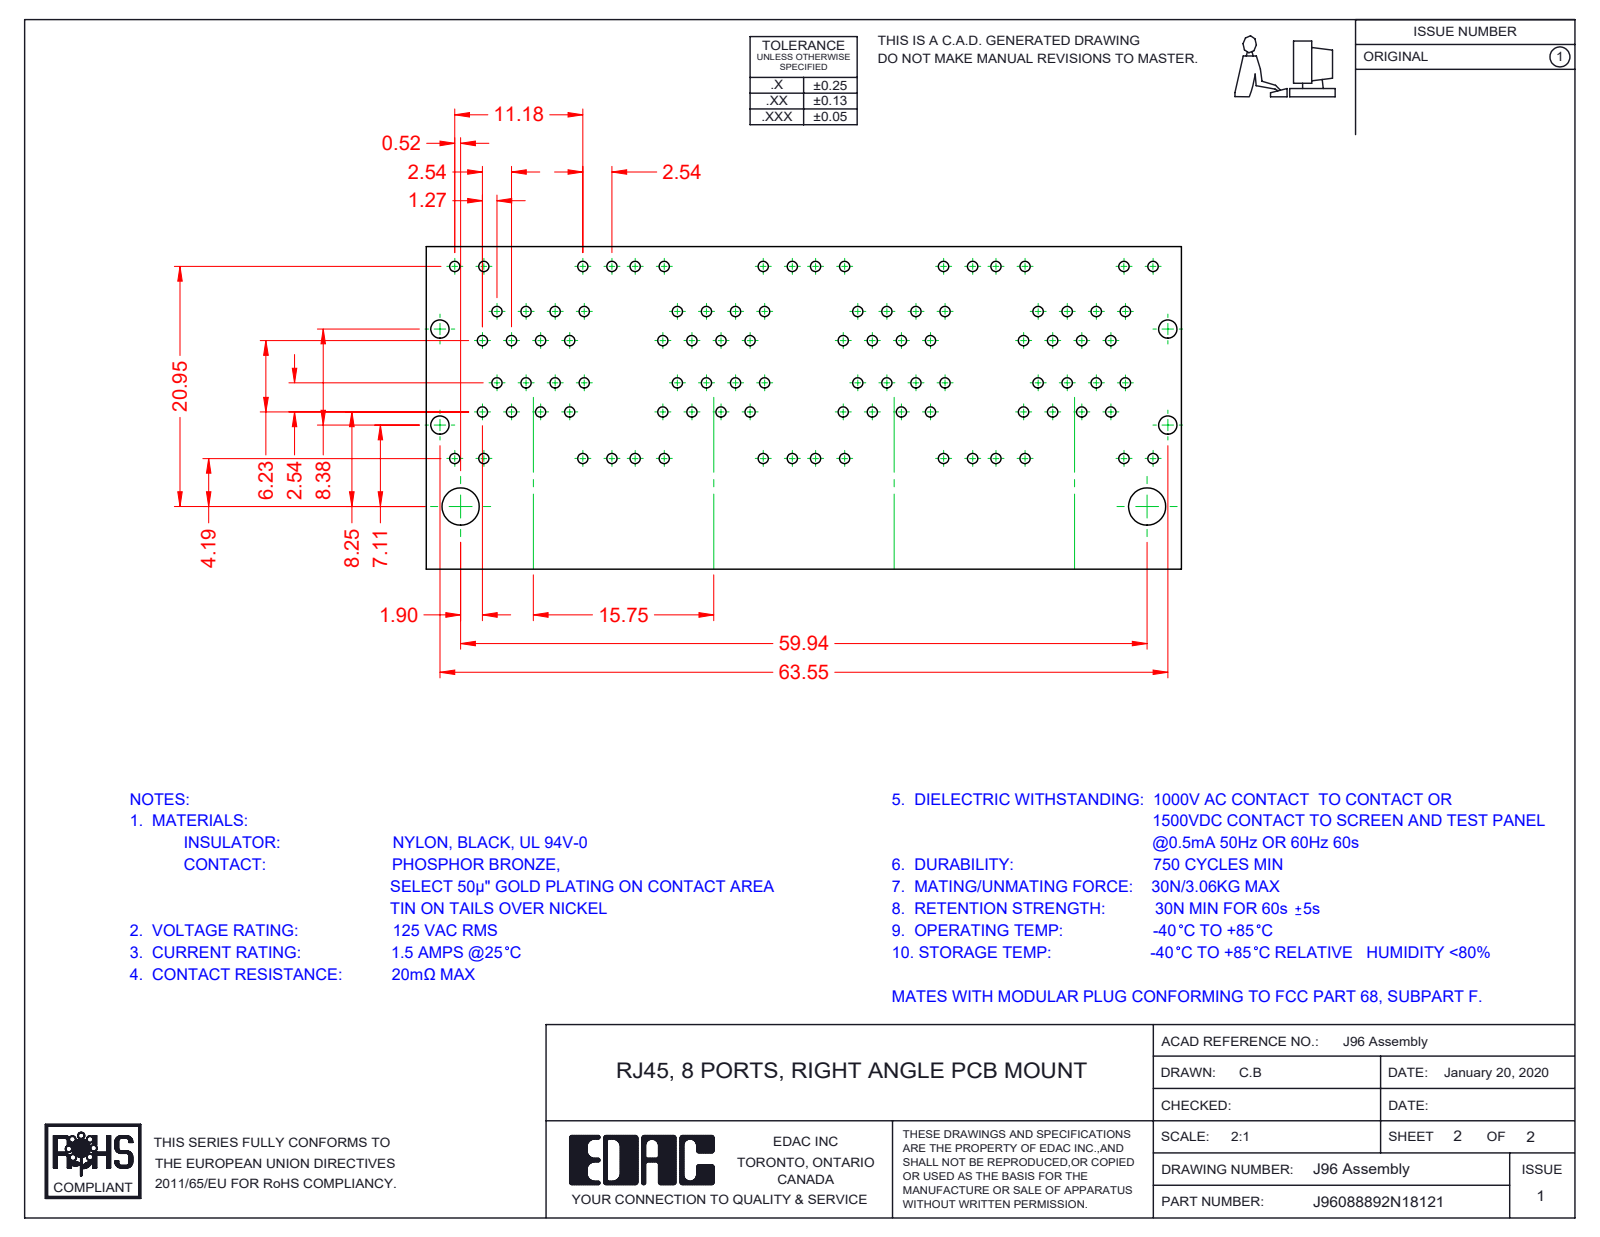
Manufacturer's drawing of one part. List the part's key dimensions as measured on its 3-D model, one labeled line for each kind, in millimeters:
Part name (STEP PRODUCT): 96 Shield_8 Ports LED - No EMI; 96 LED RH Lower_8-Red-Yellow; 96 Insulator_8 Ports; 96 Grounding_8 Ports (+8 more)
STEP written by: SolidWorks 2016 (CONFIG_CONTROL_DESIGN)
Units: millimetres
Bodies: 96 solids, 7658 faces (6069 planar, 1323 cylindrical, 266 other)
Overall size (bounding box): 64.05 × 29.58 × 28.68
Volume: 24 160 mm³ · Surface area: 63 658 mm²
Round holes (diameter × count): ⌀1.7 ×3
Round bosses / shafts (diameter × count): ⌀1.68 ×3
Partial cylindrical surfaces — rounded edges, fillets, slot ends (radius × count): R0.25 ×124, R0.35 ×73, R1 ×72, R0.5 ×49, R0.91 ×32, R0.2 ×21, R0.7 ×11, R0.22 ×8
Main face-to-face distances: 15.75, 0.35, 9.95, 1.17, 1.6, 0.54, 9.98, 10.18, 12.67, 3.37
Hole centre spacings: 15.75, 31.5
